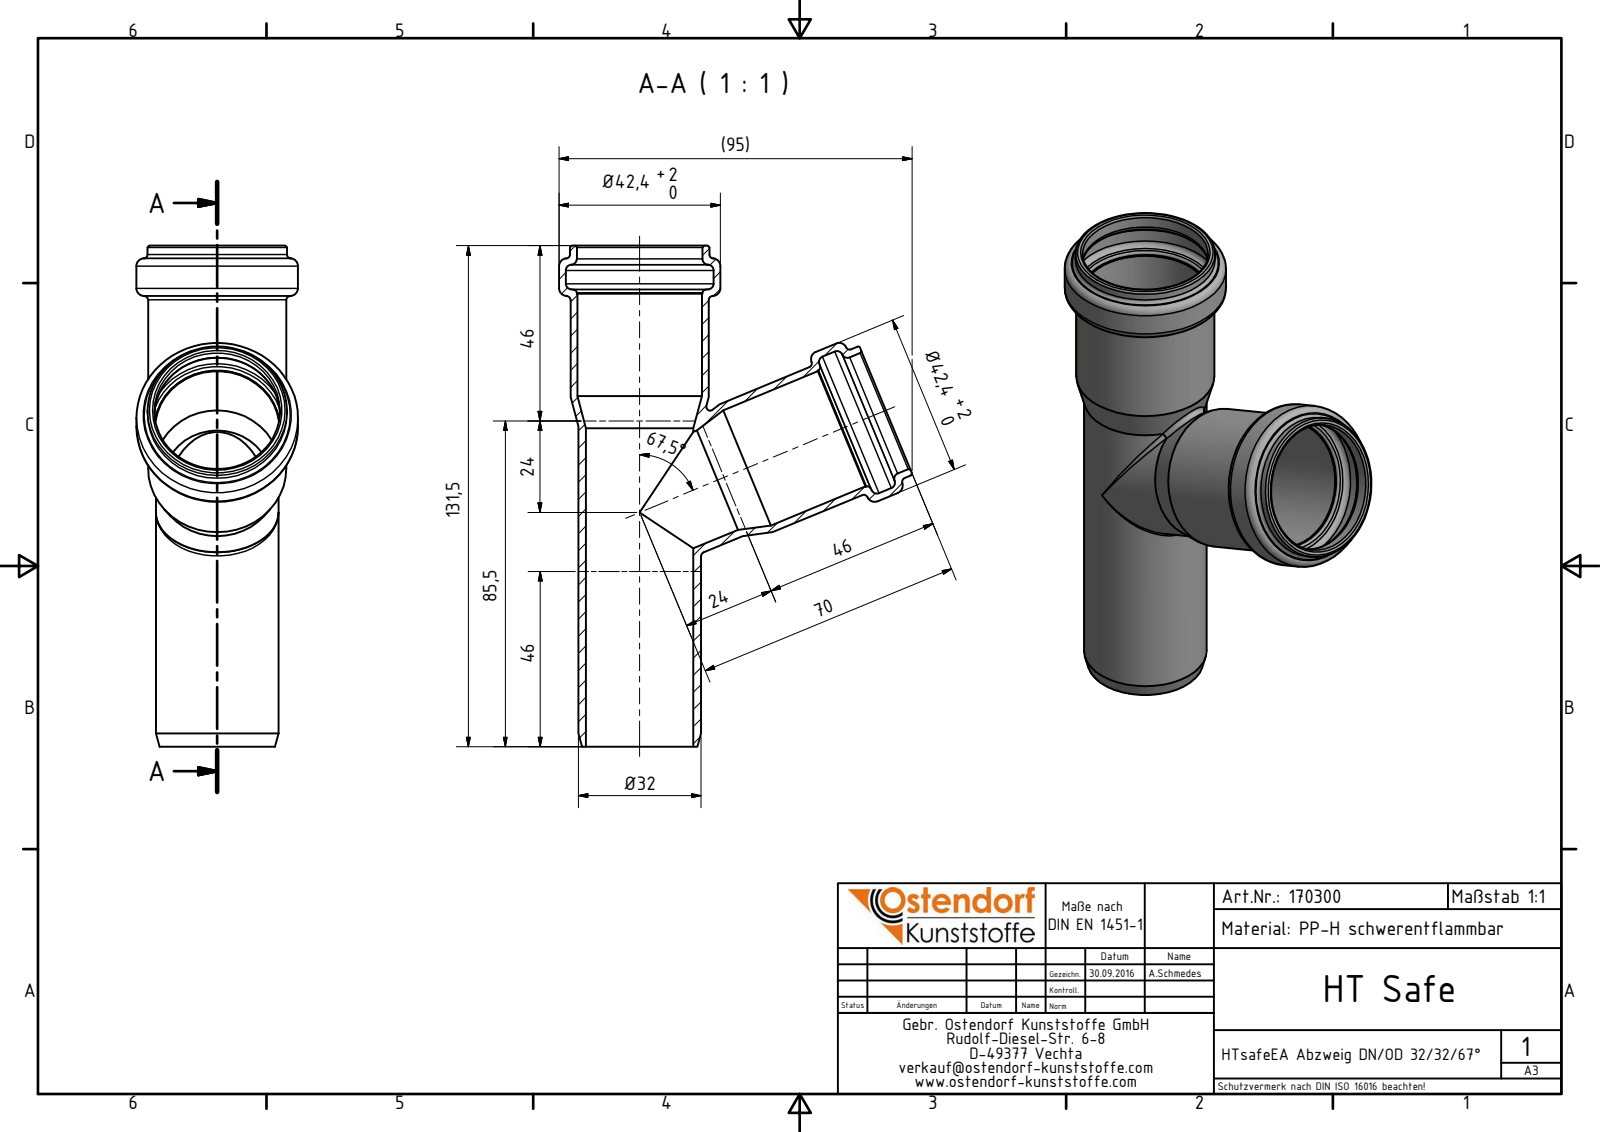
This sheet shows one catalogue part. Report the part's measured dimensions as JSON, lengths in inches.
{"part_name": "170300 HTsafeEA DN_OD 32_32_67°", "step_written_by": "Autodesk Inventor 2016 (AUTOMOTIVE_DESIGN)", "units": "inches", "bodies": {"solids": 1, "faces": 61, "planar": 5, "cylindrical": 19, "other": 37}, "overall_size": [5.177, 3.65, 1.669], "volume_in3": 2.268, "surface_area_in2": 60.96, "round_holes": [[1.299, 3], [1.11, 2], [1.287, 2], [1.528, 2]], "round_bosses_or_shafts": [[1.669, 2], [1.441, 2], [1.429, 2], [1.268, 2]], "face_to_face_distances": [5.177, 0.497, 4.68]}
